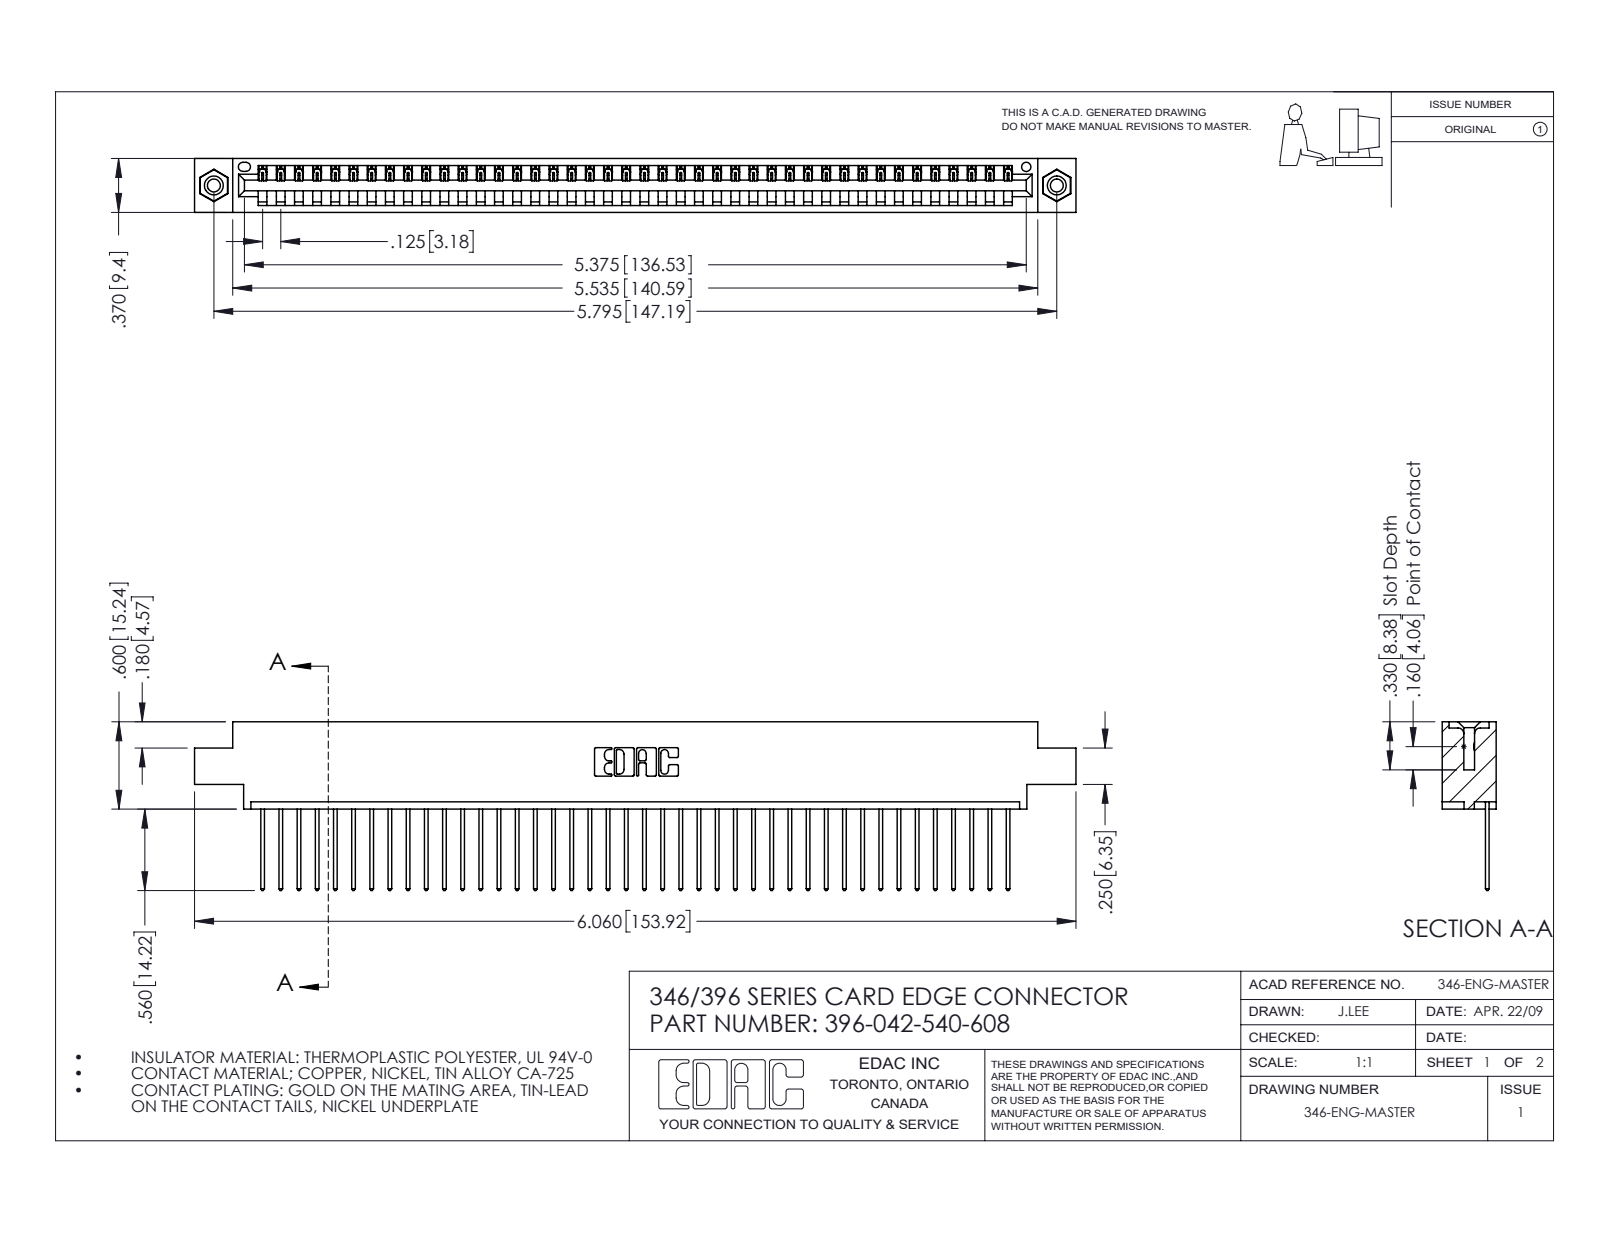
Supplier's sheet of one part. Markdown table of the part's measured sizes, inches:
| quantity | value |
| --- | --- |
| part name | 346 Part_0.170 Offset - 0.156 Dia-TI; 396-042-540-608; 345-250-001_345-250-003-102; 345-292-001_345-293-140 |
| STEP written by | SolidWorks 2016 (CONFIG_CONTROL_DESIGN) |
| units | inches |
| bodies | 45 solids, 2622 faces (1792 planar, 814 cylindrical, 16 other) |
| overall size | 6.06 × 1.16 × 0.37 |
| volume | 0.893 in³ |
| surface area | 29.27 in² |
| round holes (diameter × count) | 0.089 × 2, 0.125 × 2, 0.156 × 2, 0.064 × 1 |
| round bosses / shafts (diameter × count) | 0.155 × 2 |
| partial cylindrical surfaces (radius × count) | 0.006 × 84, 0.01 × 84, 0.01 × 22, 0.007 × 6, 0.031 × 6, 0.026 × 3, 0.031 × 2, 0.04 × 2 |
| main face-to-face distances | 0.048, 0.322, 0.37, 0.25, 0.072, 0.298, 0.025, 0.222, 0.148, 0.1 |
| hole center spacings | 0.246, 5.586, 5.795 |
